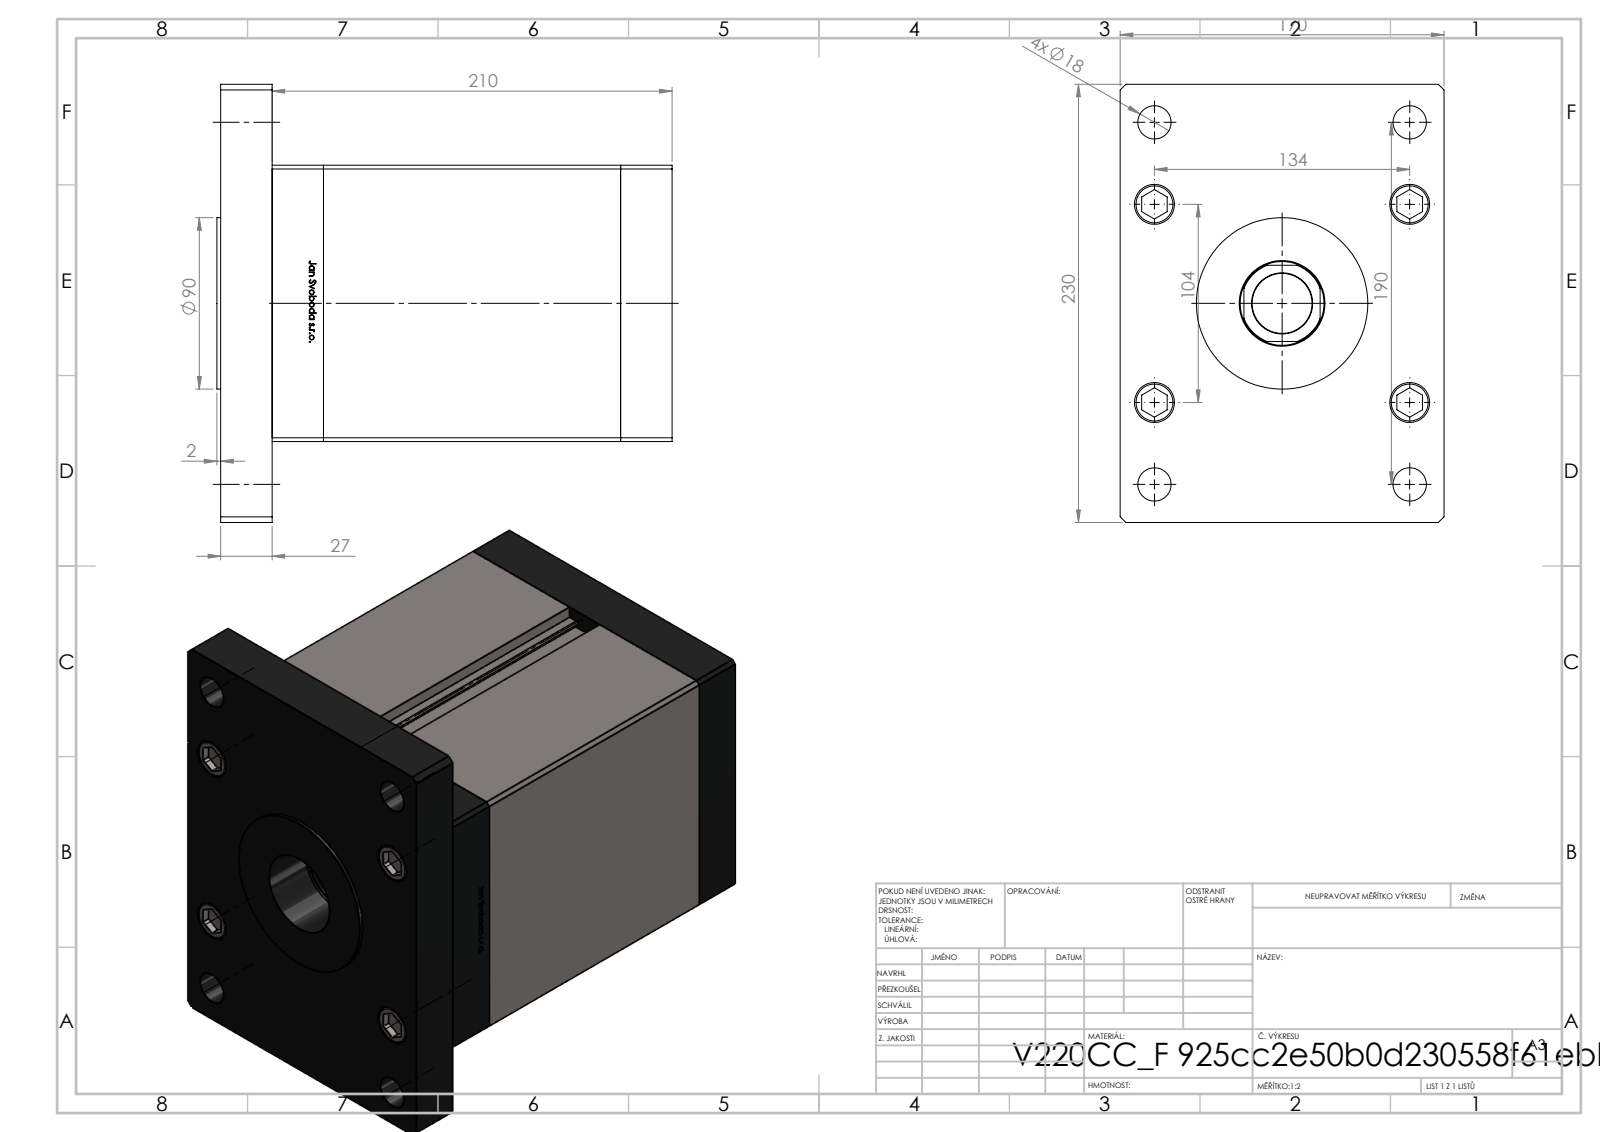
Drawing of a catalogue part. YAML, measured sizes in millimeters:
part_name: "V220C_F_MIDDLE; V220C_FRONT_F; V220C BACK_F; V220C_F (+2 more)"
step_written_by: "SolidWorks 2019 (CONFIG_CONTROL_DESIGN)"
units: millimeters
bodies: {solids: 19, faces: 1310, planar: 517, cylindrical: 187, other: 606}
overall_size: [239, 230, 170]
volume: 5300000
surface_area: 542405
round_holes:
  - {diameter: 17.5, count: 9}
  - {diameter: 22, count: 5}
  - {diameter: 16, count: 4}
  - {diameter: 21, count: 4}
  - {diameter: 2, count: 2}
  - {diameter: 13.16, count: 2}
  - {diameter: 31.5, count: 1}
  - {diameter: 45, count: 1}
  - {diameter: 46.5, count: 1}
round_bosses_or_shafts:
  - {diameter: 8, count: 9}
  - {diameter: 21, count: 5}
  - {diameter: 100, count: 1}
  - {diameter: 90, count: 1}
partial_cylinders:
  - {radius: 0.93, count: 2}
  - {radius: 22, count: 1}
face_to_face_distances: [27, 183, 210, 170, 145, 156, 54, 237, 34.8, 7.8]
hole_center_spacings: [61, 43, 84.81, 116.25, 134, 140.73, 147, 198.91]
